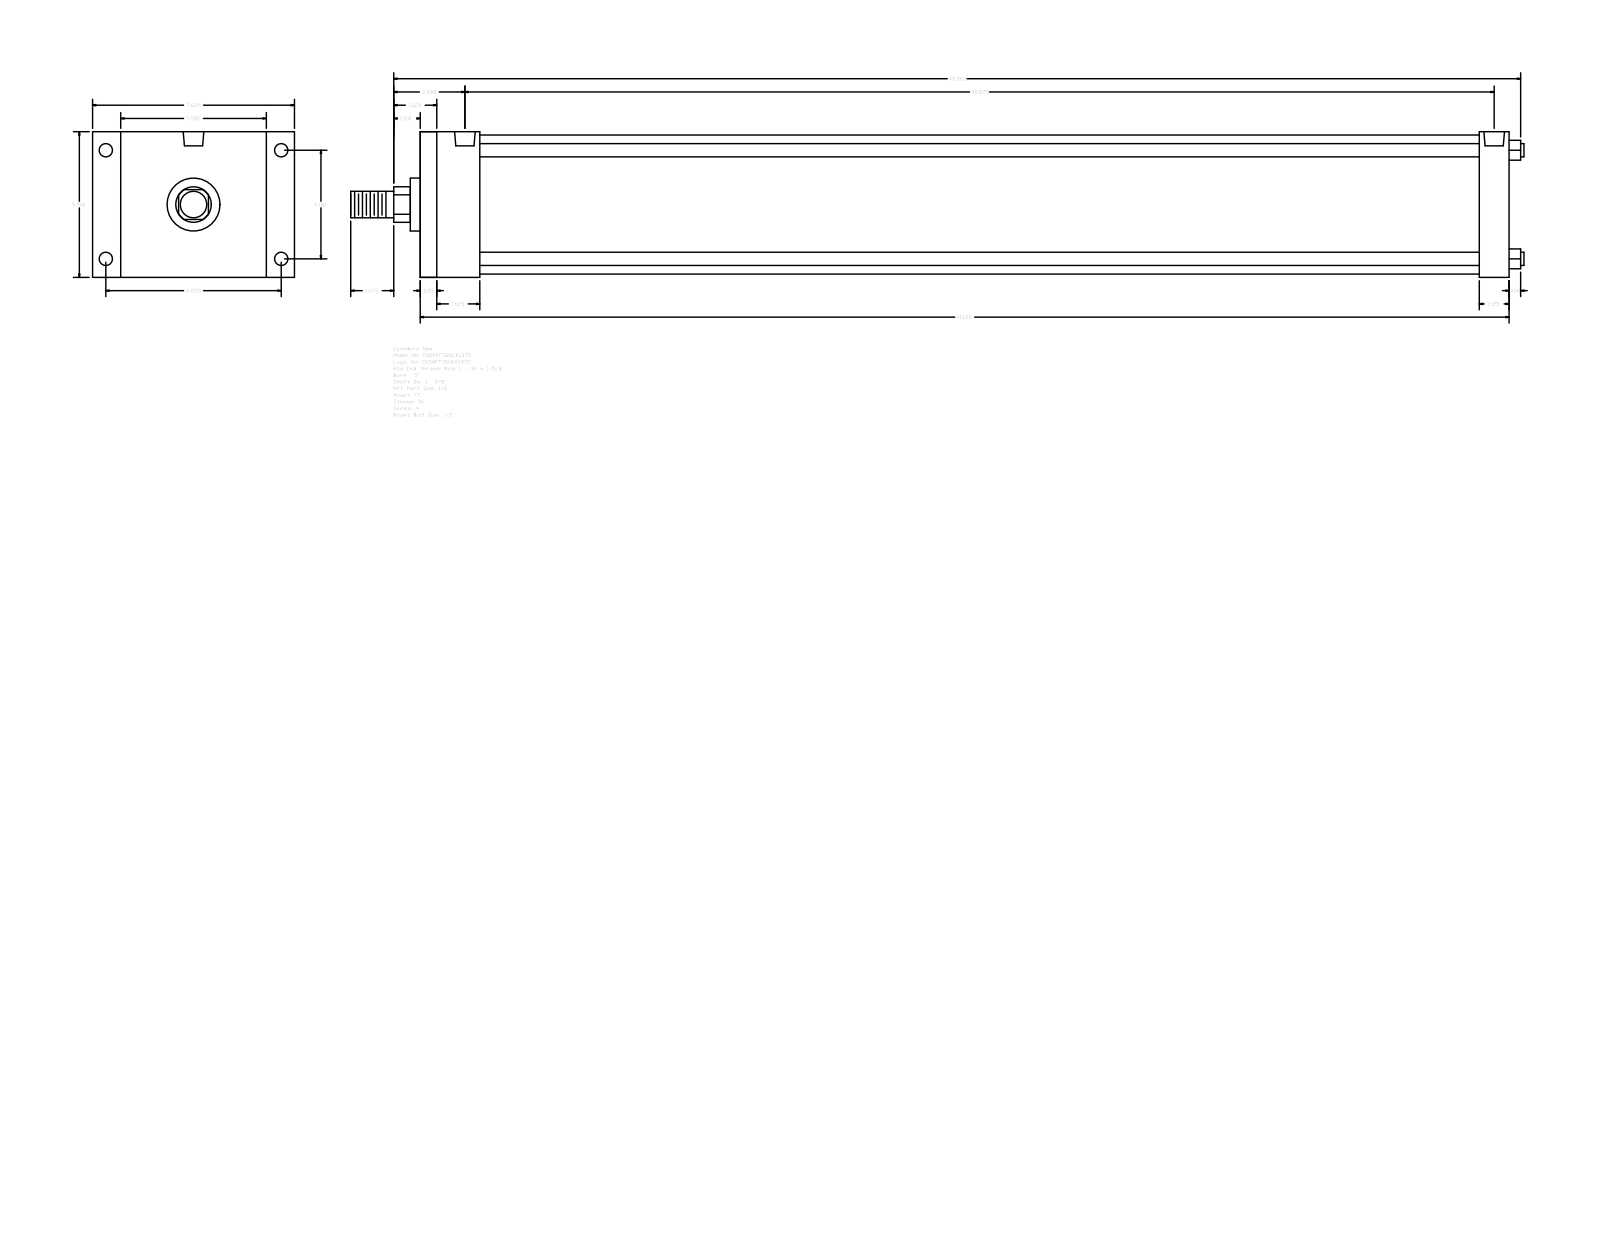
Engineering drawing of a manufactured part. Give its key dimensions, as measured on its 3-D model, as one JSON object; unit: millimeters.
{"part_name": "A_FF__0500_1.375", "step_written_by": "GSSL Pune (CONFIG_CONTROL_DESIGN)", "units": "millimeters", "bodies": {"solids": 0, "faces": 92, "planar": 64, "cylindrical": 28, "other": 0}, "overall_size": [1125.54, 193.68, 139.7], "round_holes": [[8.73, 4], [12.7, 4], [19.77, 2]], "round_bosses_or_shafts": [[12.7, 4], [133.35, 1], [50.8, 1], [34.92, 1], [25.4, 1]], "partial_cylinders_radius": [[17.06, 1]], "face_to_face_distances": [139.7, 1044.57, 1028.7, 15.87, 57.15, 28.57, 1016, 1000.13, 41.28, 958.85], "hole_center_spacings": [2.39, 104.14, 168.28, 197.9, 982.65, 985.04, 987.43]}
